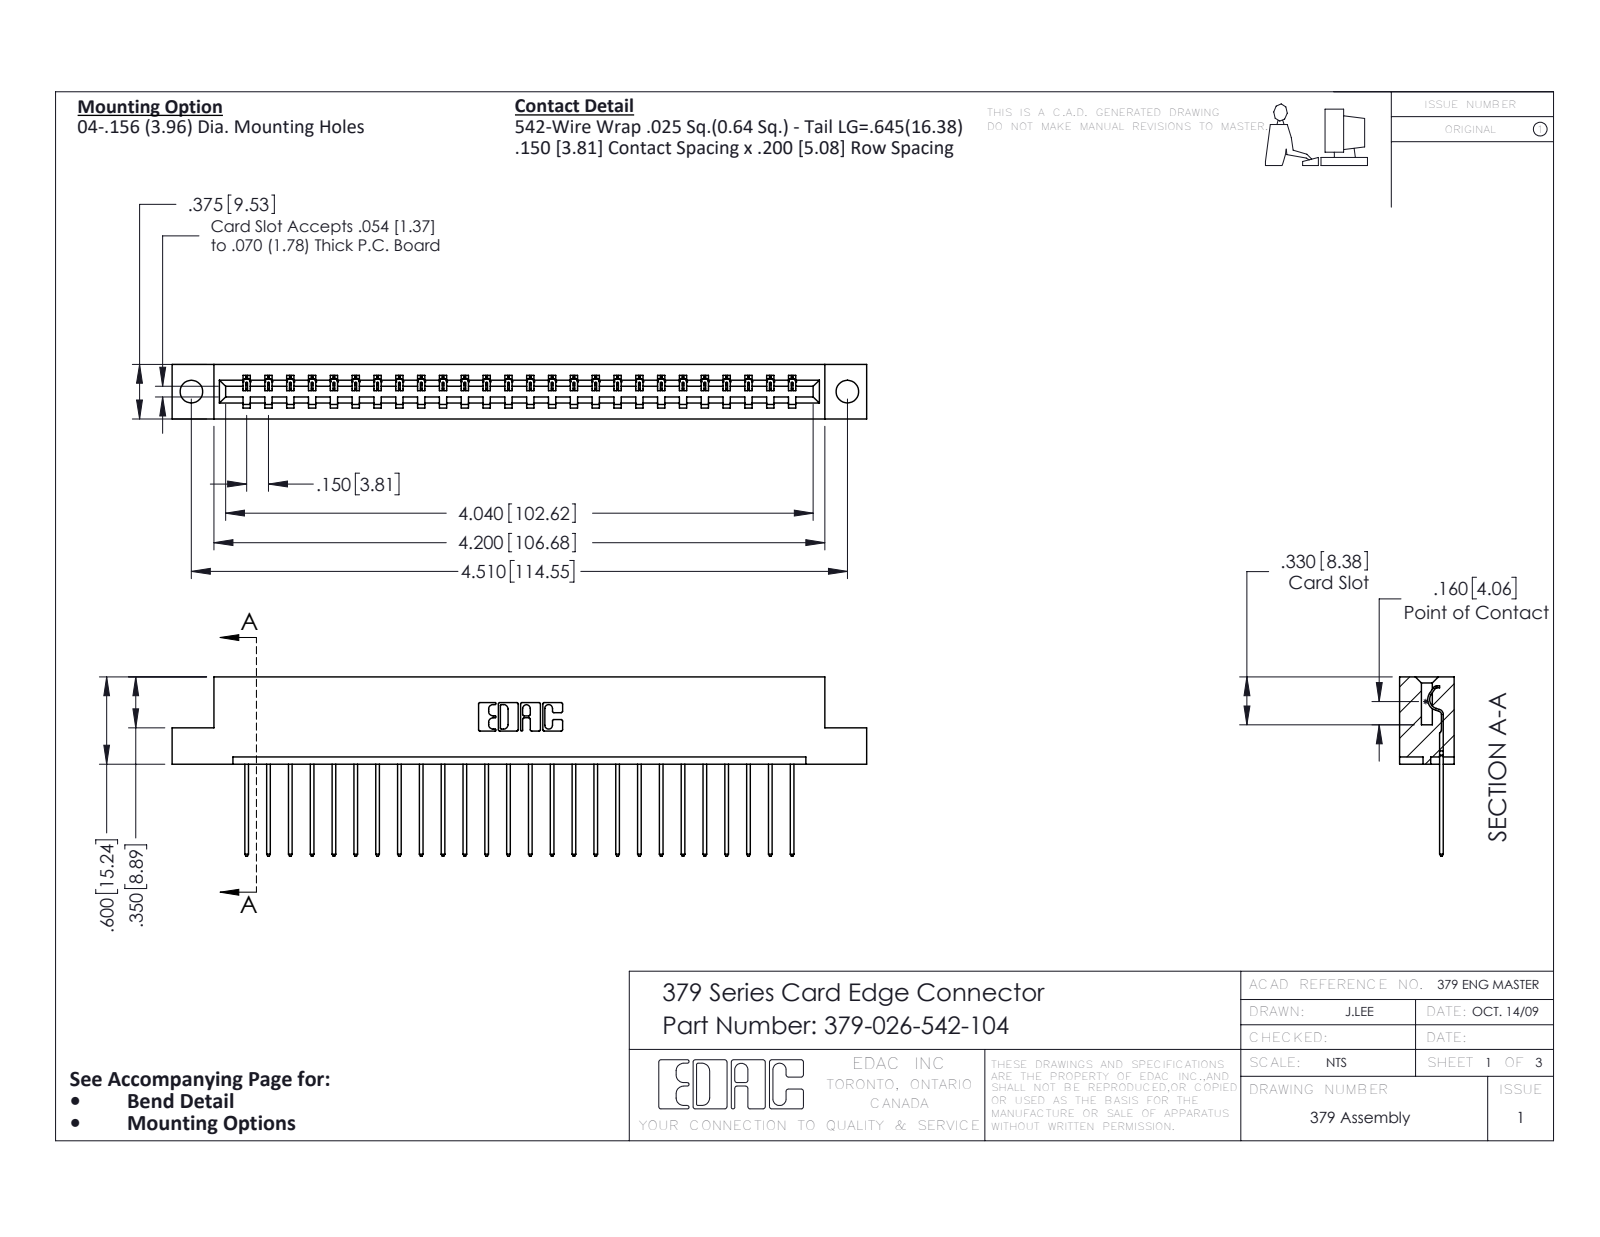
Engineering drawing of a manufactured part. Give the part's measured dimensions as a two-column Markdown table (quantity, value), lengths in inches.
| quantity | value |
| --- | --- |
| part name | 379-026-542-104; 345-292-001_345-293-142; 379 Part_Flush - .156 Dia - TH |
| STEP written by | SolidWorks 2016 (CONFIG_CONTROL_DESIGN) |
| units | inches |
| bodies | 27 solids, 1622 faces (1162 planar, 460 cylindrical, 0 other) |
| overall size | 4.775 × 1.232 × 0.375 |
| volume | 0.764 in³ |
| surface area | 20.01 in² |
| round holes (diameter × count) | 0.156 × 2 |
| partial cylindrical surfaces (radius × count) | 0.006 × 52, 0.01 × 52, 0.01 × 22, 0.007 × 6, 0.031 × 6, 0.026 × 3, 0.014 × 1, 0.022 × 1 |
| main face-to-face distances | 0.3, 0.075, 0.375, 0.225, 0.6, 0.275, 0.1, 0.025, 0.2, 0.15 |
| hole center spacings | 4.51 |
